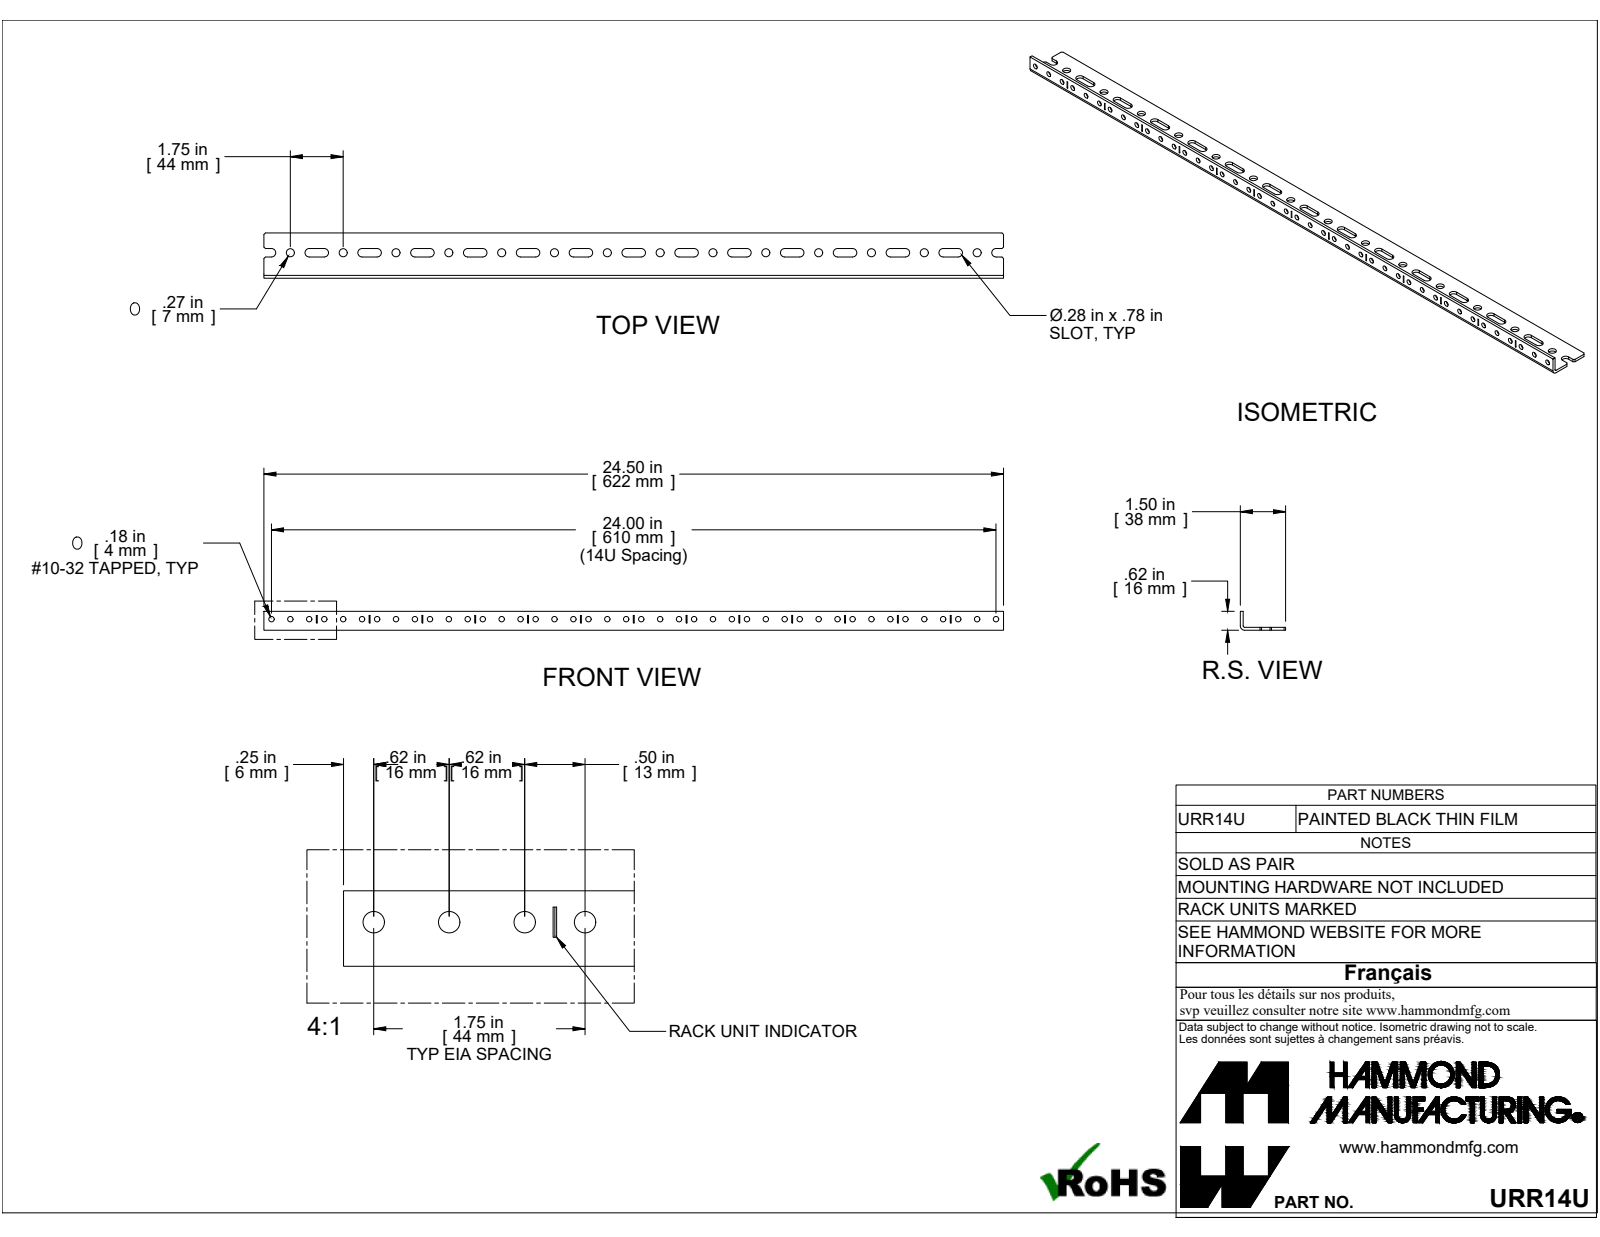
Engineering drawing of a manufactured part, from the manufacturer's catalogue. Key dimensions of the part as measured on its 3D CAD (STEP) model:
Part name (STEP PRODUCT): COM57213-14
STEP written by: ST-DEVELOPER v16.7 (AUTOMOTIVE_DESIGN)
Units: millimetres
Bodies: 1 solid, 184 faces (98 planar, 86 cylindrical, 0 other)
Overall size (bounding box): 622.3 × 38.1 × 15.88
Volume: 68 598 mm³ · Surface area: 63 905 mm²
Round holes (diameter × count): ⌀4.5 ×42, ⌀6.76 ×14
Partial cylindrical surfaces — rounded edges, fillets, slot ends (radius × count): R3.57 ×28, R1.22 ×1, R3.63 ×1
Main face-to-face distances: 2.41, 15.88, 13.47, 38.1, 35.69, 17.84, 24.98, 15.43, 22.57, 7.14
Hole centre spacings: 88.9, 44.45, 133.35, 177.8, 266.7, 15.87, 15.88, 31.75
